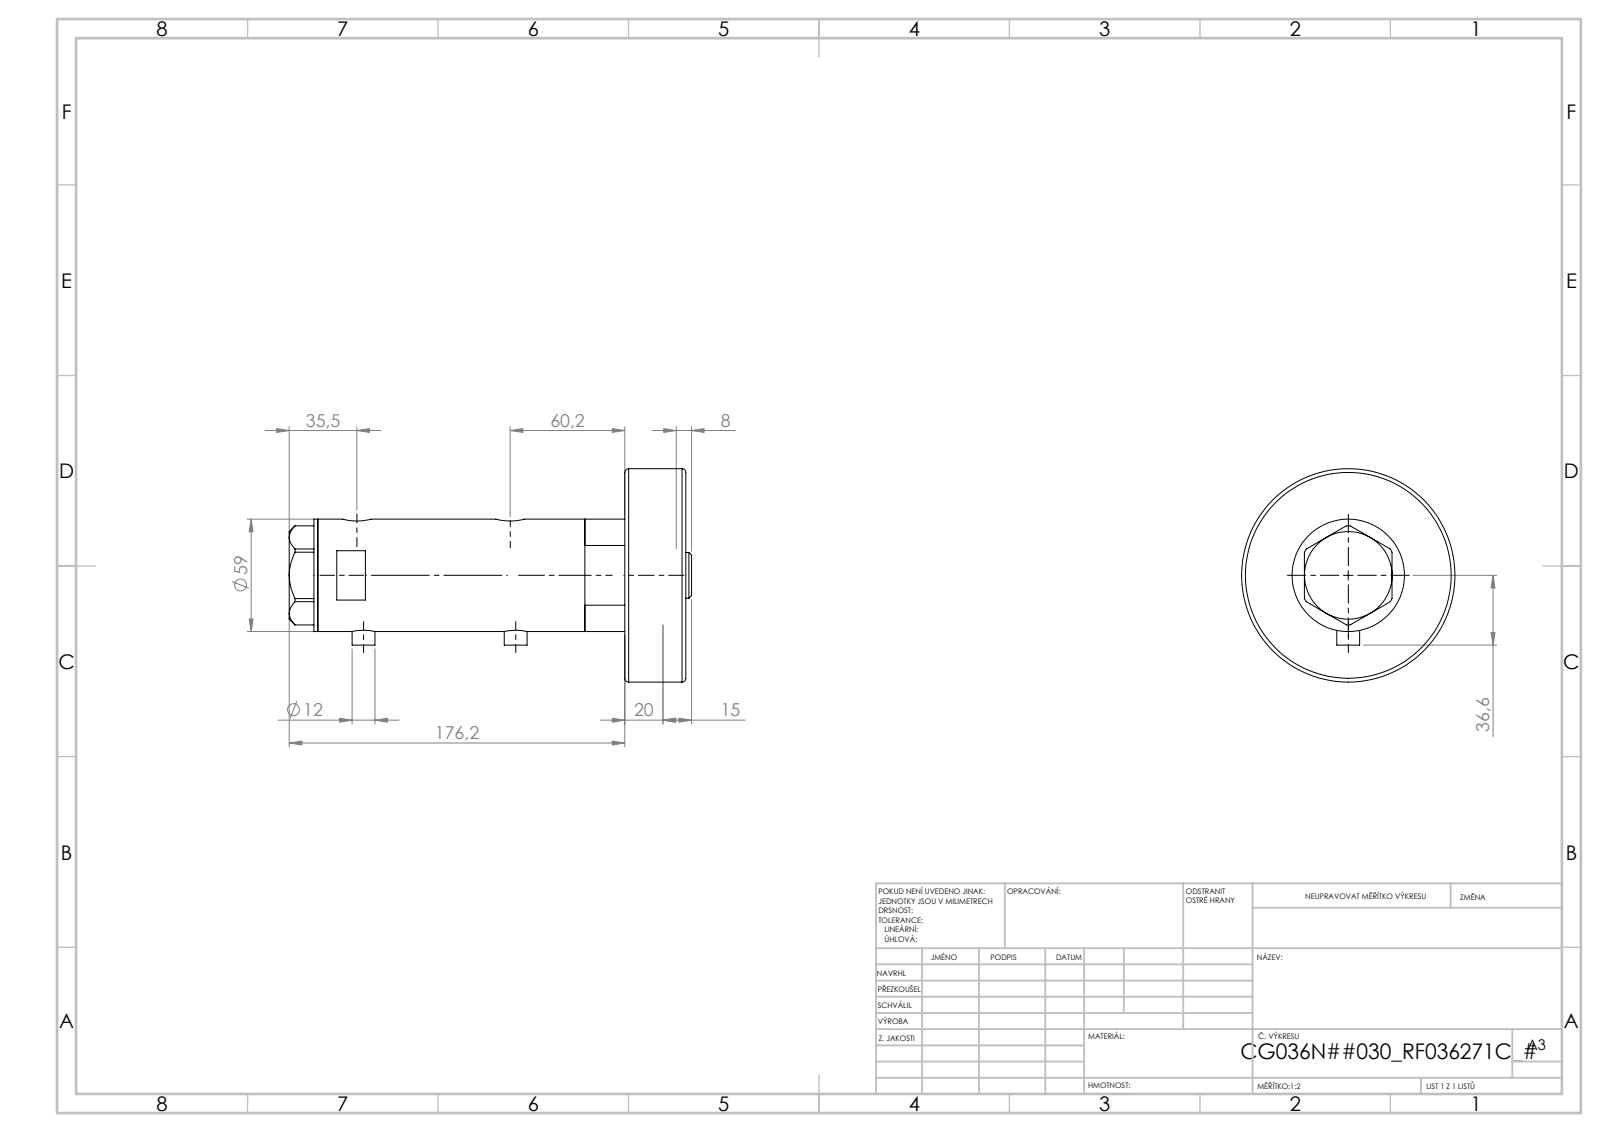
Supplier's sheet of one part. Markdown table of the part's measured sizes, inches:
| quantity | value |
| --- | --- |
| part name | V270CG_BACK; V270CG_271C; V270CG_MIDDLE; V270CG_FRONT (+1 more) |
| STEP written by | SolidWorks 2019 (CONFIG_CONTROL_DESIGN) |
| units | inches |
| bodies | 5 solids, 136 faces (55 planar, 57 cylindrical, 24 other) |
| overall size | 7.615 × 4.409 × 4.409 |
| volume | 42.36 in³ |
| surface area | 193.4 in² |
| round holes (diameter × count) | 0.197 × 2, 0.383 × 2, 0.492 × 2, 0.591 × 2, 0.335 × 1, 0.984 × 1, 1.043 × 1, 1.417 × 1, 1.575 × 1, 1.89 × 1, 2.047 × 1 |
| round bosses / shafts (diameter × count) | 0.472 × 2, 4.409 × 1, 2.323 × 1, 1.811 × 1, 0.945 × 1 |
| main face-to-face distances | 1.26, 5.545, 6.805, 3.439, 2.106, 3.366, 0.925, 2.513, 4.62, 5.88 |
| hole center spacings | 0.114, 0.138, 2.447, 2.561, 2.585, 2.699, 0.114, 0.115 |
